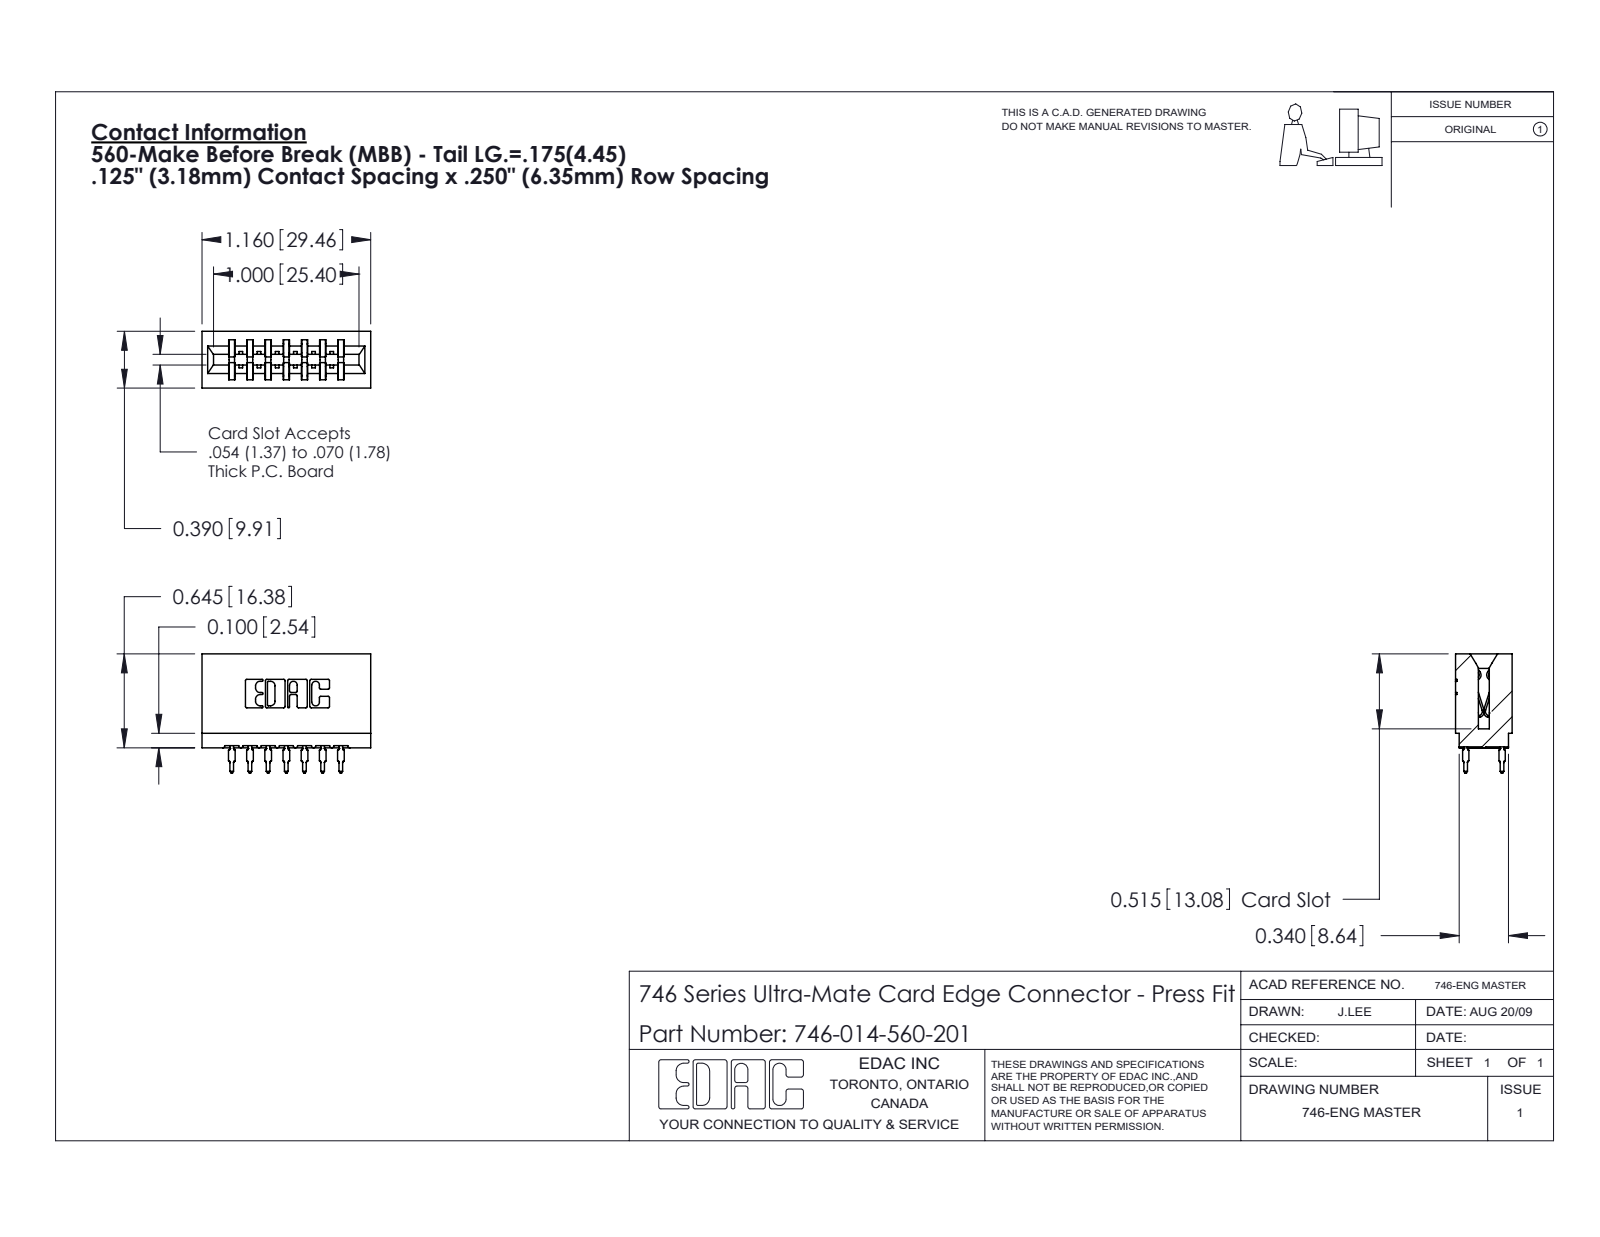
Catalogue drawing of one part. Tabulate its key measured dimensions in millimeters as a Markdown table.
| quantity | value |
| --- | --- |
| part name | 746-014-560-201; 746-292-001_560; 746 Part_.515 Slot Depth - 01 |
| STEP written by | SolidWorks 2020 (CONFIG_CONTROL_DESIGN) |
| units | millimeters |
| bodies | 15 solids, 1420 faces (713 planar, 343 cylindrical, 364 other) |
| overall size | 29.5 × 20.8 × 9.9 |
| volume | 3 440 mm³ |
| surface area | 5 080 mm² |
| partial cylindrical surfaces (radius × count) | 0.5 × 28, 0.3 × 22, 0.1 × 8, 0.3 × 8, 0.4 × 8, 0.2 × 6, 0.8 × 6, 0.5 × 4 |
| main face-to-face distances | 6.4, 8.5, 1.1, 1.4, 3.2, 12.7, 3.2, 2.1, 7.4, 5.3 |
